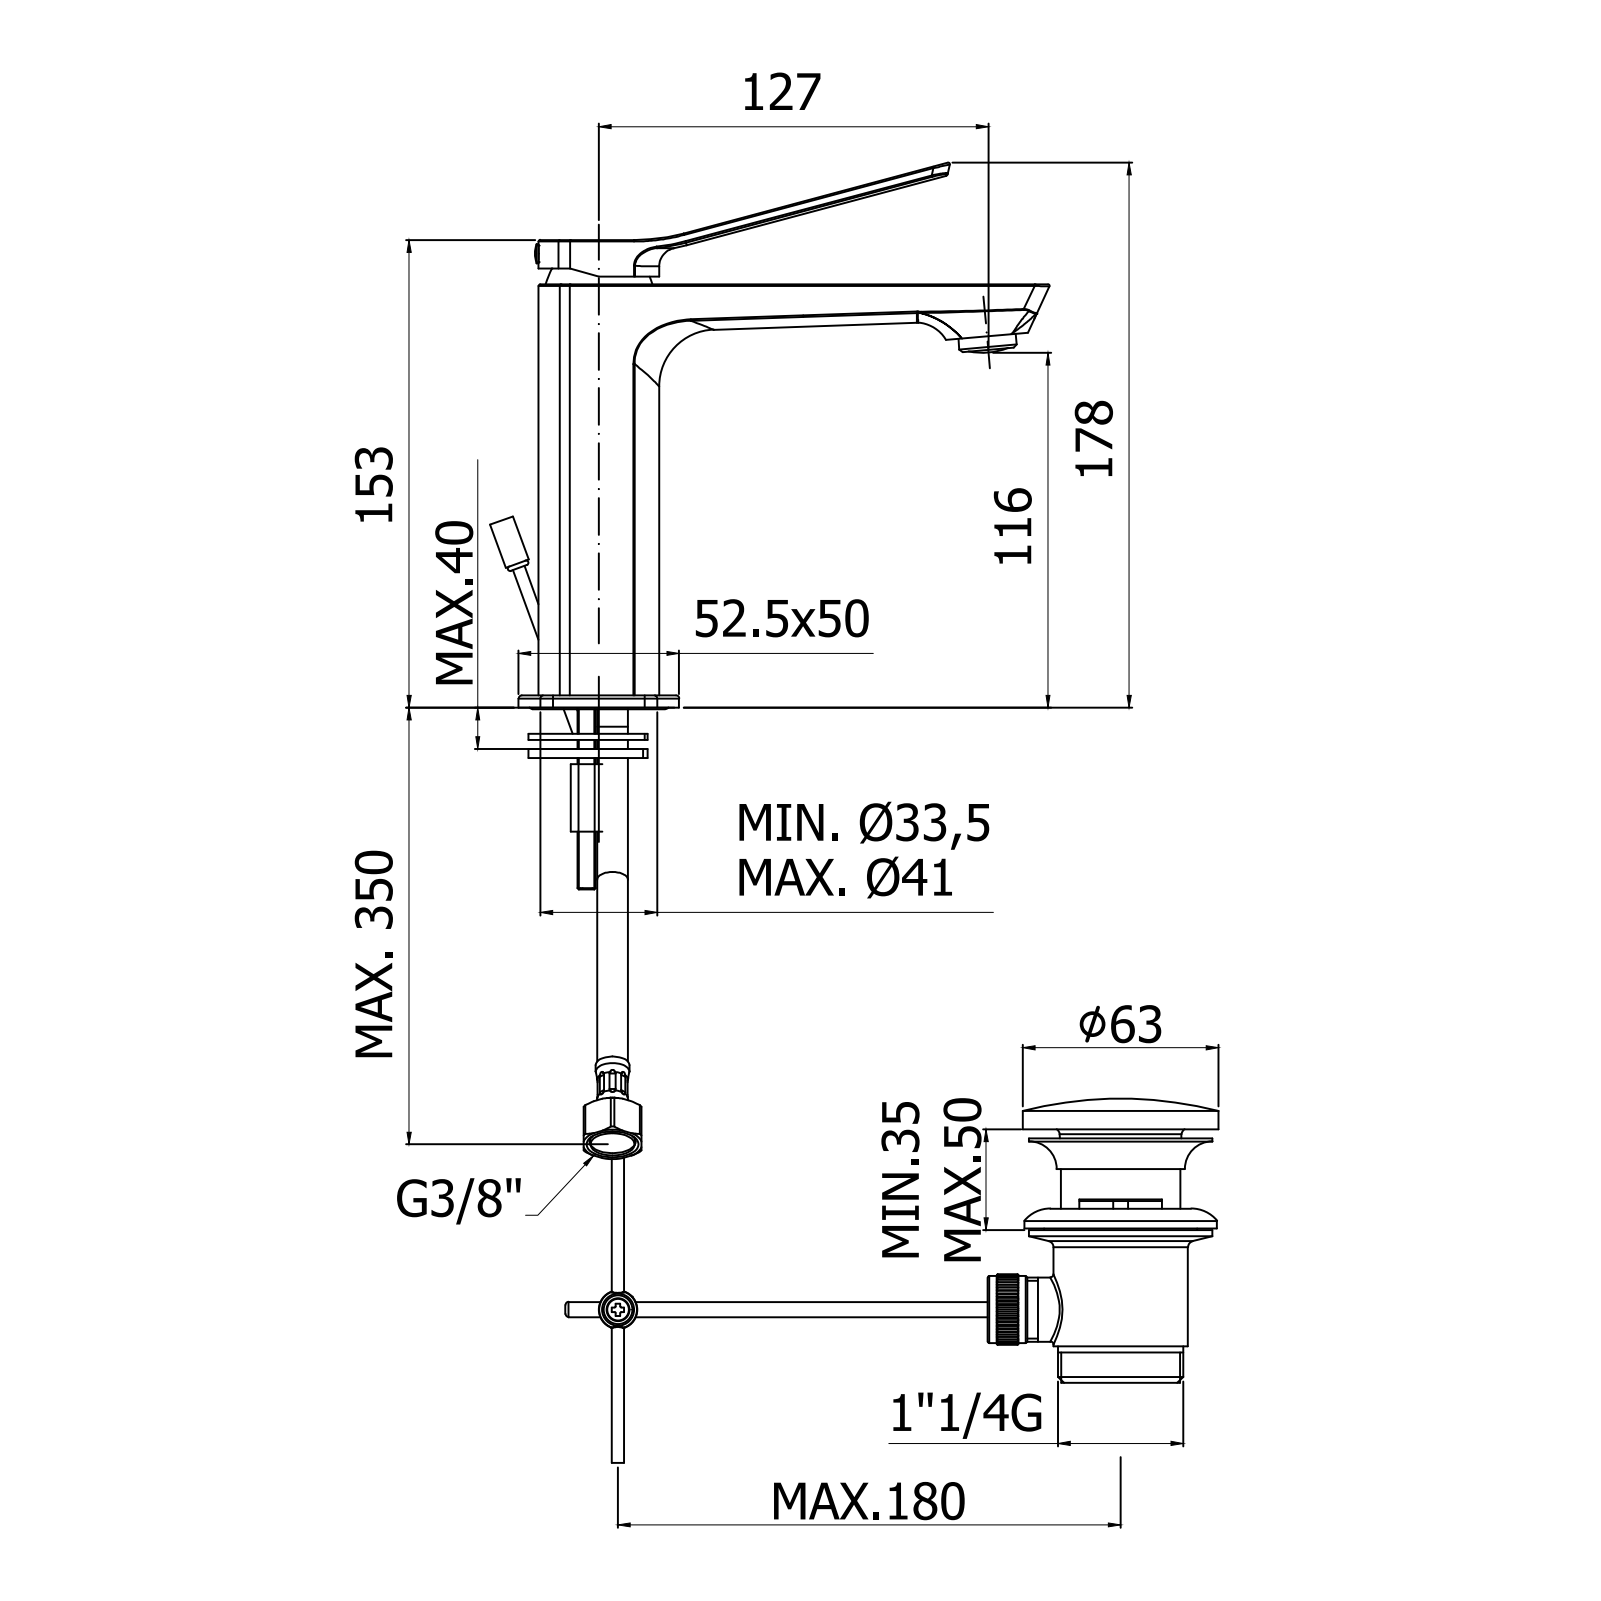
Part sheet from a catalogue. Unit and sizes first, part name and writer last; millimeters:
Units: millimetres
Overall size (bounding box): 182.99 × 178.31 × 50
Round holes (diameter × count): ⌀5 ×3, ⌀4.2 ×2, ⌀6.2 ×2, ⌀4 ×1, ⌀5.5 ×1, ⌀15 ×1, ⌀19.5 ×1, ⌀26.5 ×1, ⌀28 ×1, ⌀29 ×1, ⌀30.6 ×1, ⌀33.5 ×1
Round bosses / shafts (diameter × count): ⌀4 ×2, ⌀41 ×1, ⌀33 ×1, ⌀31.8 ×1, ⌀30.3 ×1, ⌀18.8 ×1, ⌀9.5 ×1, ⌀8 ×1
Partial cylindrical surfaces — rounded edges, fillets, slot ends (radius × count): R1 ×52, R0.5 ×20, R5 ×14, R4.5 ×4, R21.5 ×2, R24.5 ×2, R24.87 ×2, R40.09 ×2
Main face-to-face distances: 3, 135.5, 138.5, 1.5, 4, 147.5, 13, 153, 17.5, 14.5
Hole centre spacings: 11.7, 13.04, 11, 22
Volume: 120 584 mm³ · Surface area: 79 669 mm²
Bodies: 3 solids, 573 faces (115 planar, 199 cylindrical, 259 other)
Part name (STEP PRODUCT): TI075CR
STEP written by: CREO PARAMETRIC BY PTC INC, 2020044 (CONFIG_CONTROL_DESIGN)
